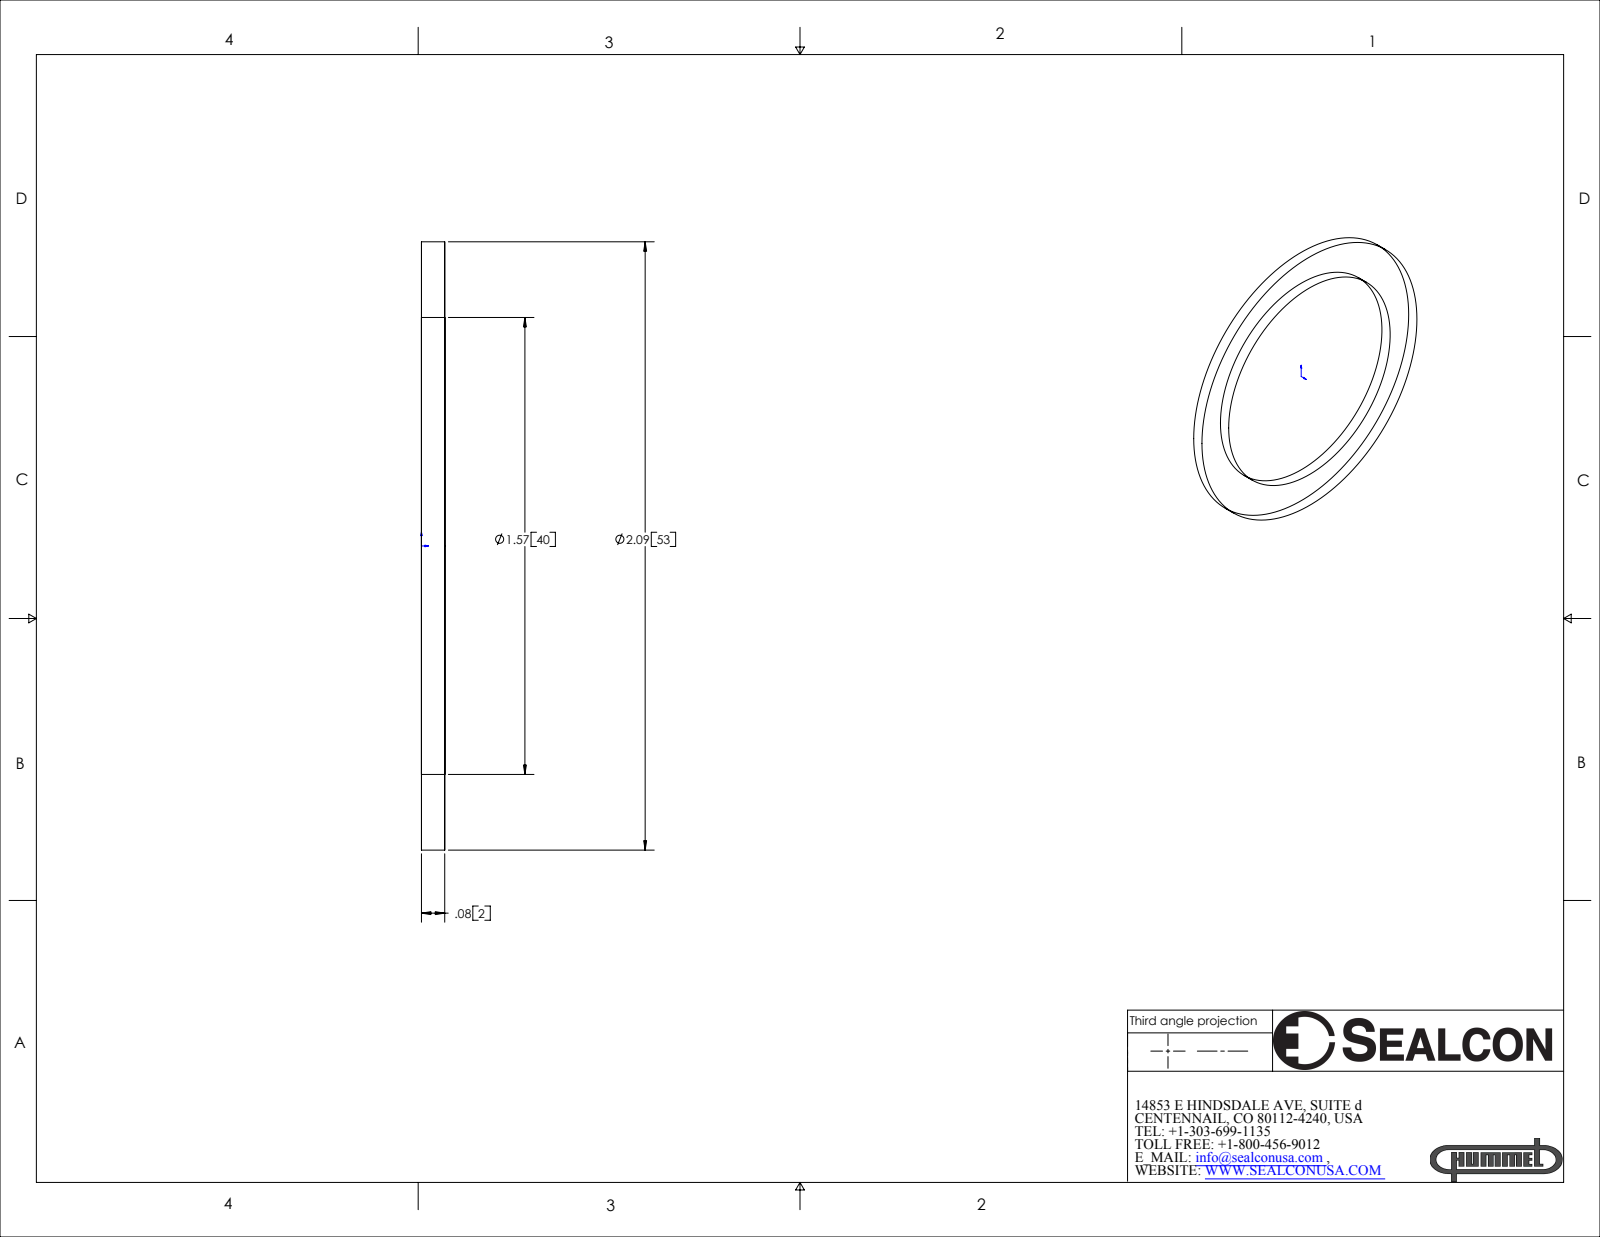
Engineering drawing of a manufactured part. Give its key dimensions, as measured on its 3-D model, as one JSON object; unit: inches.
{"part_name": "MS-40-NY", "step_written_by": "SolidWorks 2007 (CONFIG_CONTROL_DESIGN)", "units": "inches", "bodies": {"solids": 1, "faces": 6, "planar": 2, "cylindrical": 4, "other": 0}, "overall_size": [2.09, 2.09, 0.08], "volume_in3": 0.12, "surface_area_in2": 3.909, "round_holes": [[1.57, 1]], "round_bosses_or_shafts": [[2.09, 1]], "face_to_face_distances": [0.08]}
